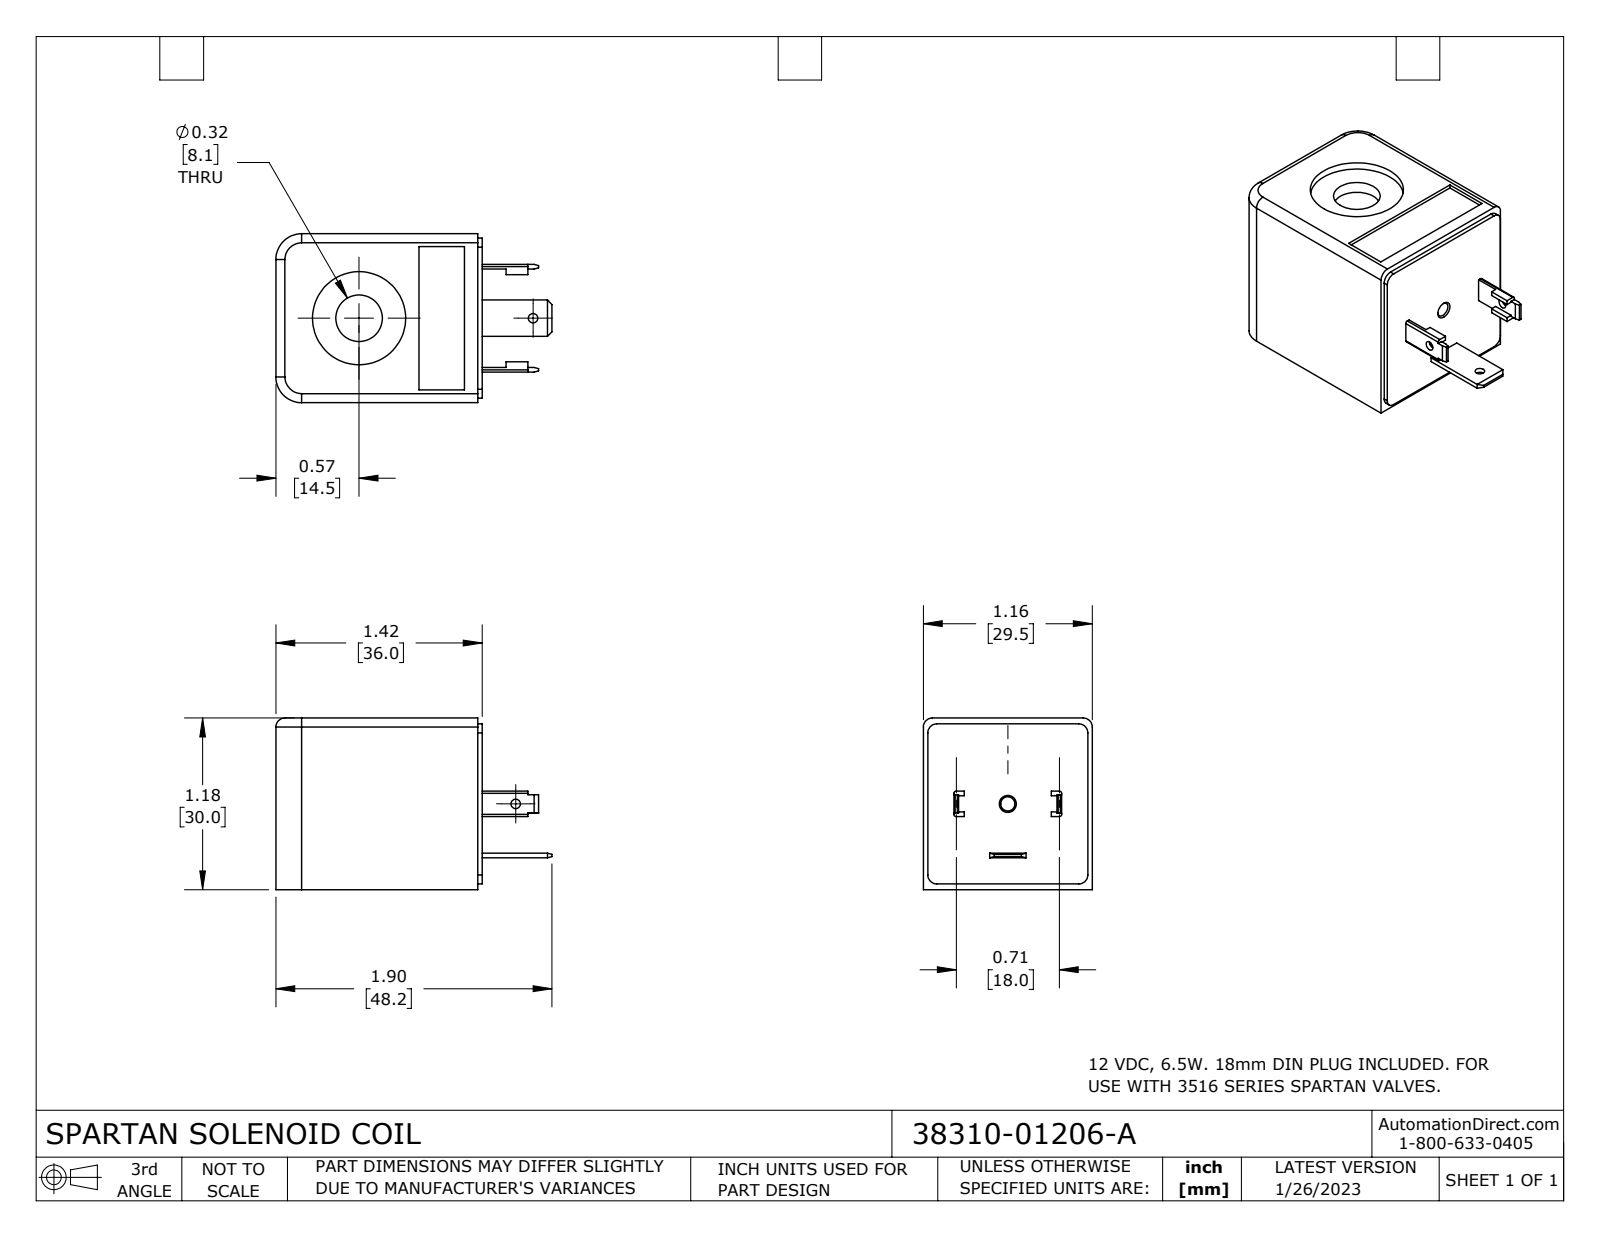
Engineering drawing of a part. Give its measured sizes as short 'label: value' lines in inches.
name: 38310-01206-A
written by: SolidWorks 2021 (CONFIG_CONTROL_DESIGN)
unit: in
bodies: 1 solid, 97 faces (62 planar, 29 cylindrical, 6 other)
size: 1.898 × 1.181 × 1.161
volume: 1.788 in³; area: 11.02 in²
holes: 2× ⌀0.065, 1× ⌀0.097, 1× ⌀0.32, 1× ⌀0.36, 1× ⌀0.435, 1× ⌀0.64
rounds: 7× R0.062, 4× R0.015, 2× R0.177
face distances: 1.161, 1.418, 1.181, 1.156, 0.025, 1.129, 0.027, 0.052, 0.03, 1.388
hole spacings: 1.196
